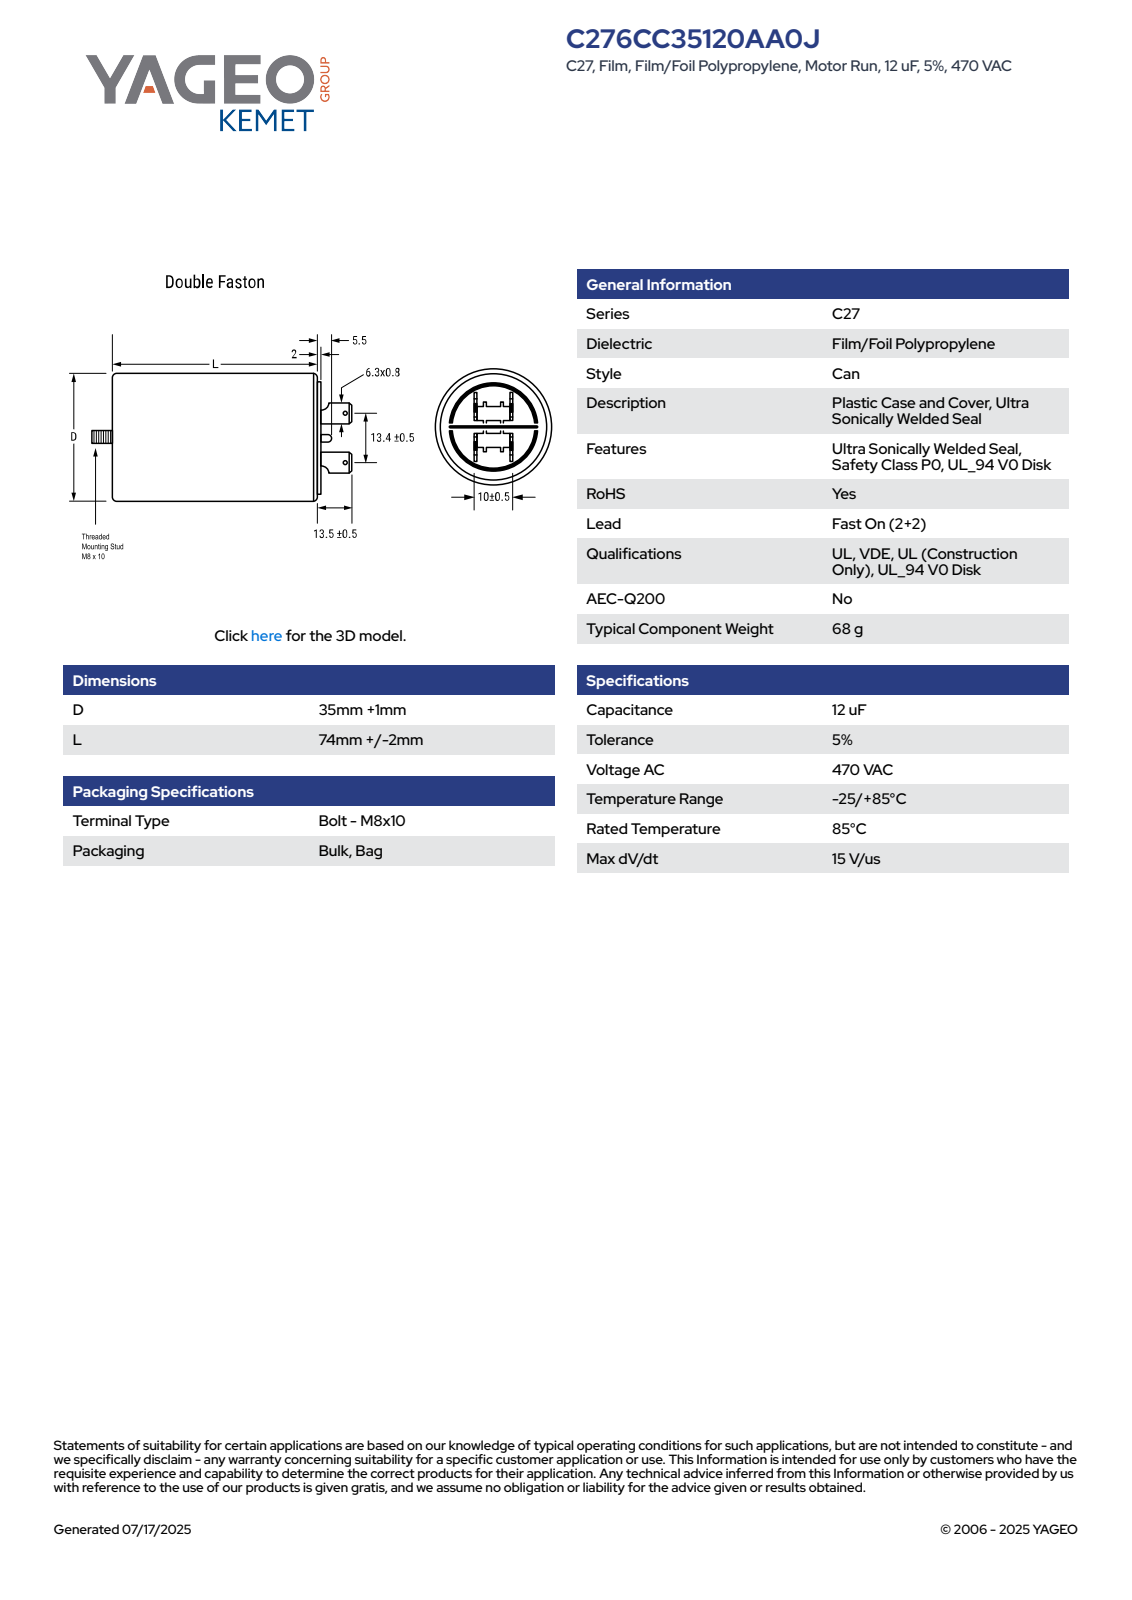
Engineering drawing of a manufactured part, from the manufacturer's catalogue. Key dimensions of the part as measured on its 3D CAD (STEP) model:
Part name (STEP PRODUCT): CFM_C27DF_35X74_D36L76
STEP written by: SolidWorks 2014 (AUTOMOTIVE_DESIGN)
Units: millimetres
Bodies: 1 solid, 137 faces (49 planar, 53 cylindrical, 35 other)
Overall size (bounding box): 100 × 36 × 36
Volume: 79 147 mm³ · Surface area: 11 707 mm²
Round holes (diameter × count): ⌀1.2 ×2
Round bosses / shafts (diameter × count): ⌀36 ×1, ⌀27.69 ×1, ⌀8 ×1
Partial cylindrical surfaces — rounded edges, fillets, slot ends (radius × count): R0.25 ×9, R4 ×2, R17.99 ×1
Main face-to-face distances: 78, 0.8, 9.7, 76, 2, 8.9, 10.5, 0.5, 10, 86
Hole centre spacings: 13.9
